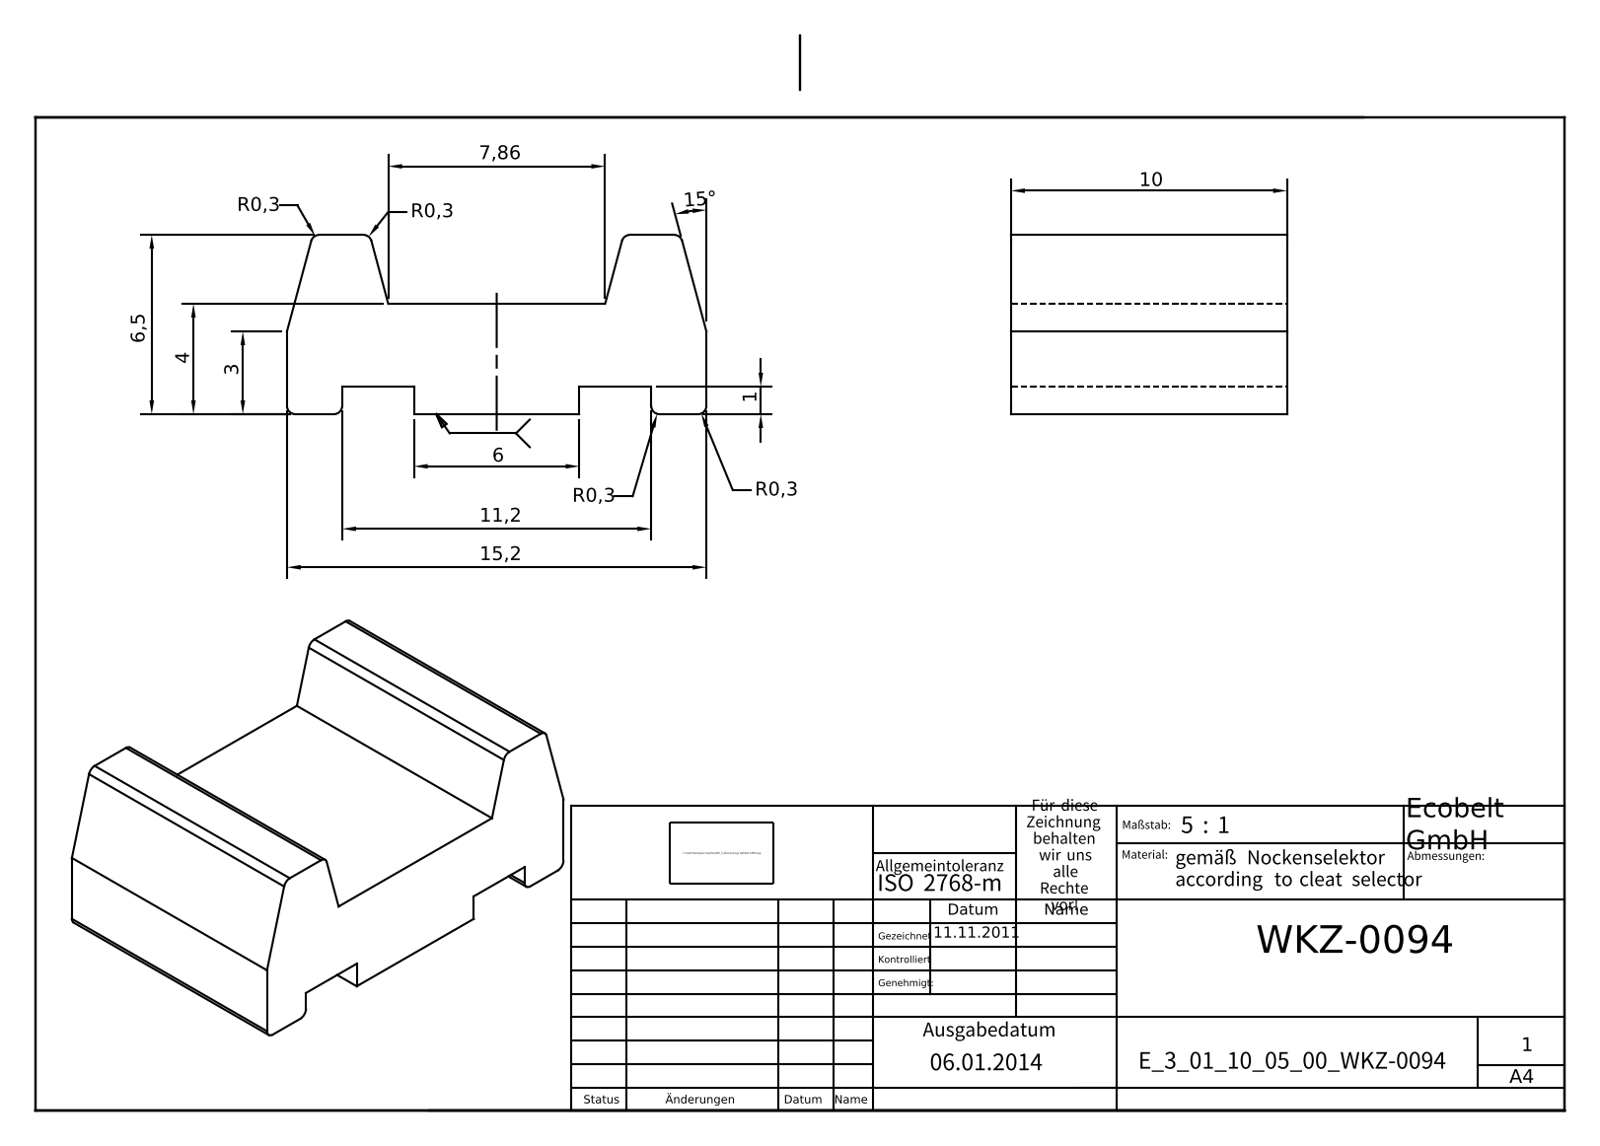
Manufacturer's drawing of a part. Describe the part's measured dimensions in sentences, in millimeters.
The part is named "E_3_01_10_05_00_WKZ-0094". Its 3-D file was written by "Autodesk Inventor 2025 (AUTOMOTIVE_DESIGN)". It is 1 solid with 28 faces: 20 planar, 8 cylindrical and 0 other. Overall it measures 15.2 by 10 by 6.5 millimeters. Its volume is 689 cubic millimeters and its surface area 626 square millimeters. Partial cylindrical surfaces (rounded edges, fillets, slot ends): 8 of radius 0.3. The main face-to-face distances are 4, 10, 1, 3, 10.88, 6.5, 5.5, 2.5, 15.2, 4.6.
